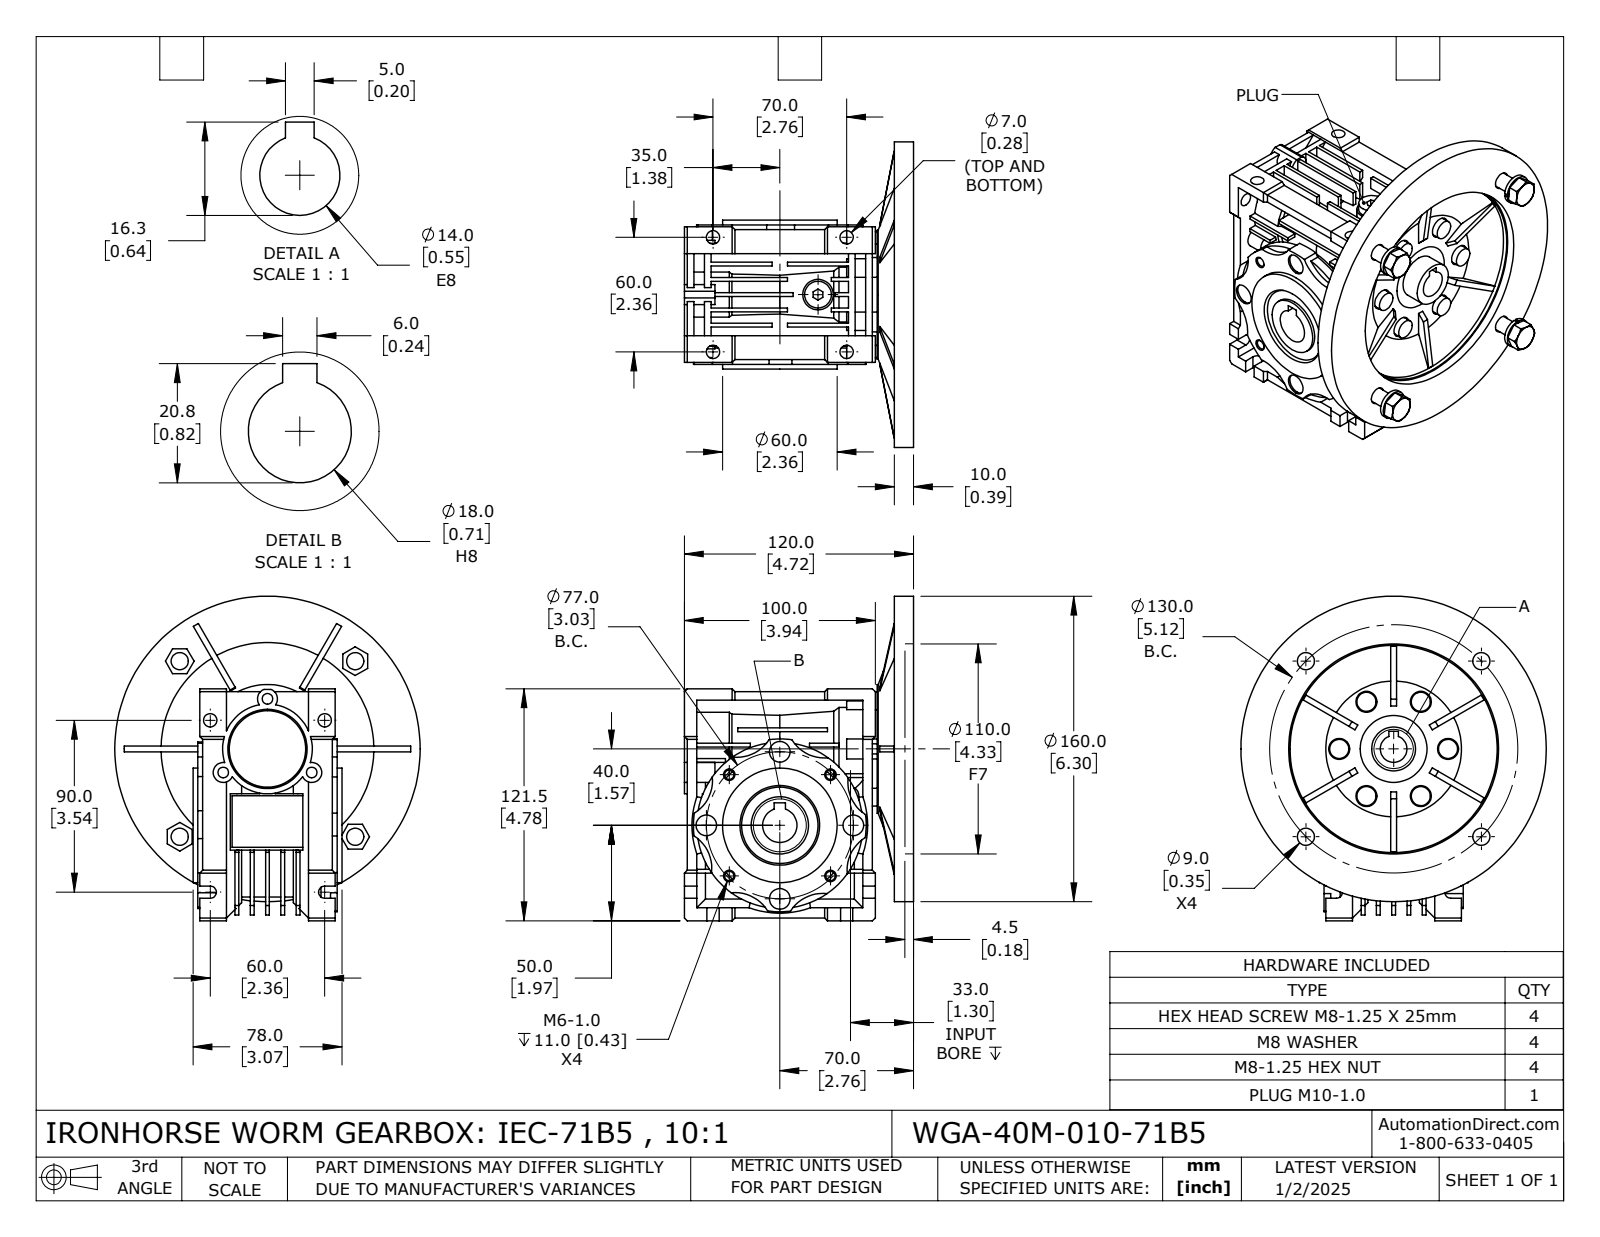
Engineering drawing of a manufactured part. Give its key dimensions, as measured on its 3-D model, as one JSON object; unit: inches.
{"part_name": "WGA-40M-010-71B5", "step_written_by": "SolidWorks 2024 (CONFIG_CONTROL_DESIGN)", "units": "inches", "bodies": {"solids": 18, "faces": 1101, "planar": 630, "cylindrical": 290, "other": 181}, "overall_size": [6.693, 6.299, 5.42], "volume_in3": 47.6, "surface_area_in2": 313.1, "round_holes": [[0.276, 6], [0.433, 6], [0.354, 5], [0.194, 4], [0.268, 4], [0.315, 4], [0.323, 4], [0.425, 4], [0.219, 3], [0.551, 1], [0.591, 1], [0.709, 1]], "round_bosses_or_shafts": [[0.394, 6], [0.606, 4], [6.299, 1], [2.953, 1], [2.657, 1], [2.362, 1], [2.126, 1], [1.85, 1]], "partial_cylinders_radius": [[0.787, 8], [0.126, 6], [0.206, 6], [0.207, 3], [1.713, 1], [1.716, 1], [1.781, 1], [1.811, 1]], "face_to_face_distances": [0.394, 0.315, 0.079, 0.236, 0.197, 0.059, 0.63, 0.945, 0.551, 0.098], "hole_center_spacings": [1.122, 1.146, 2.765, 1.943, 1.32, 1.476, 1.504, 1.516]}
